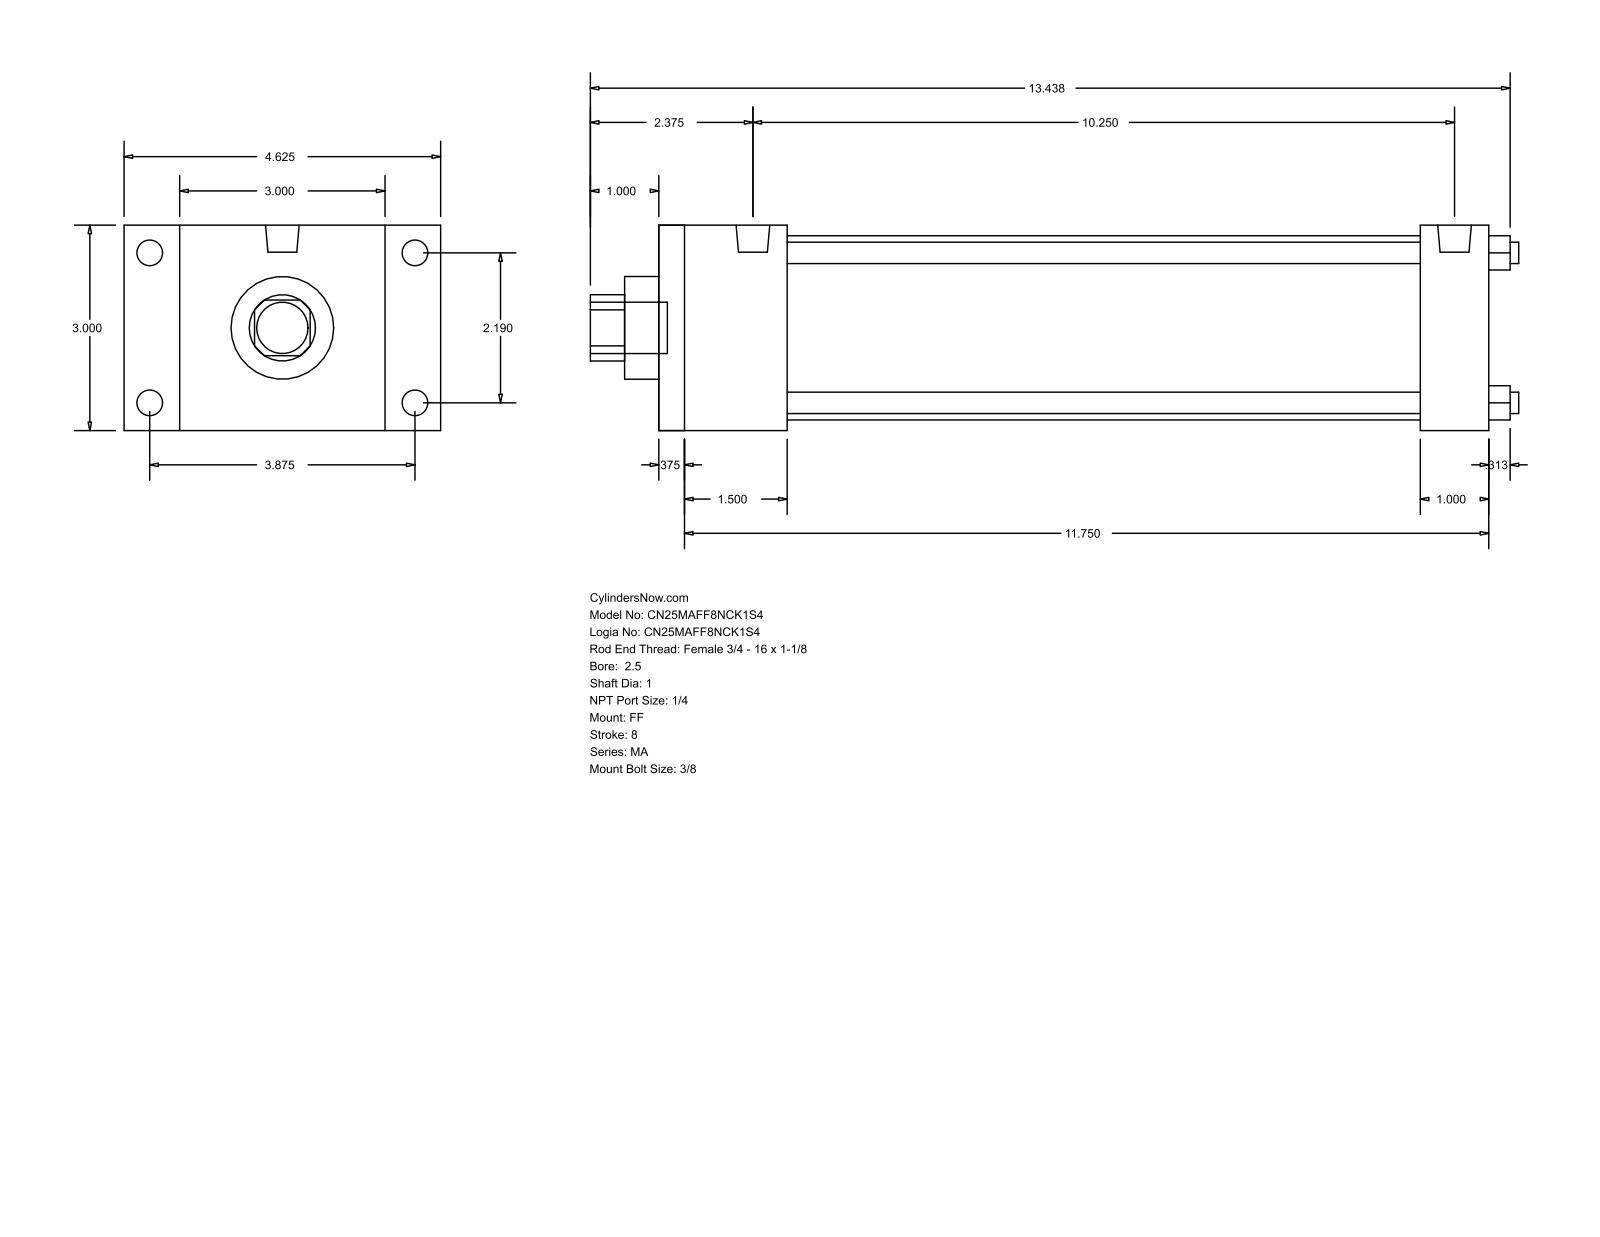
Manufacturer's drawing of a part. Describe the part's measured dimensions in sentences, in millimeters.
The part is named "MA_FF__0250_1". Its 3-D file was written by "GSSL Pune (CONFIG_CONTROL_DESIGN)". It is 0 solids with 92 faces: 64 planar, 28 cylindrical and 0 other. Overall it measures 344.49 by 117.47 by 76.2 millimeters. Round holes: 4 of diameter 7.94, 1 of diameter 25.4, 1 of diameter 38.1, 1 of diameter 68.33. Round bosses or shafts: 4 of diameter 9.53, 4 of diameter 7.94, 2 of diameter 12.49, 1 of diameter 19.05. Partial cylindrical surfaces (rounded edges, fillets, slot ends): 1 of radius 12.29. The main face-to-face distances are 76.2, 307.98, 9.52, 298.46, 25.4, 47.63, 282.58, 38.11, 273.06, 234.95. The hole center spacings are 39.33, 55.62, 78.66.
